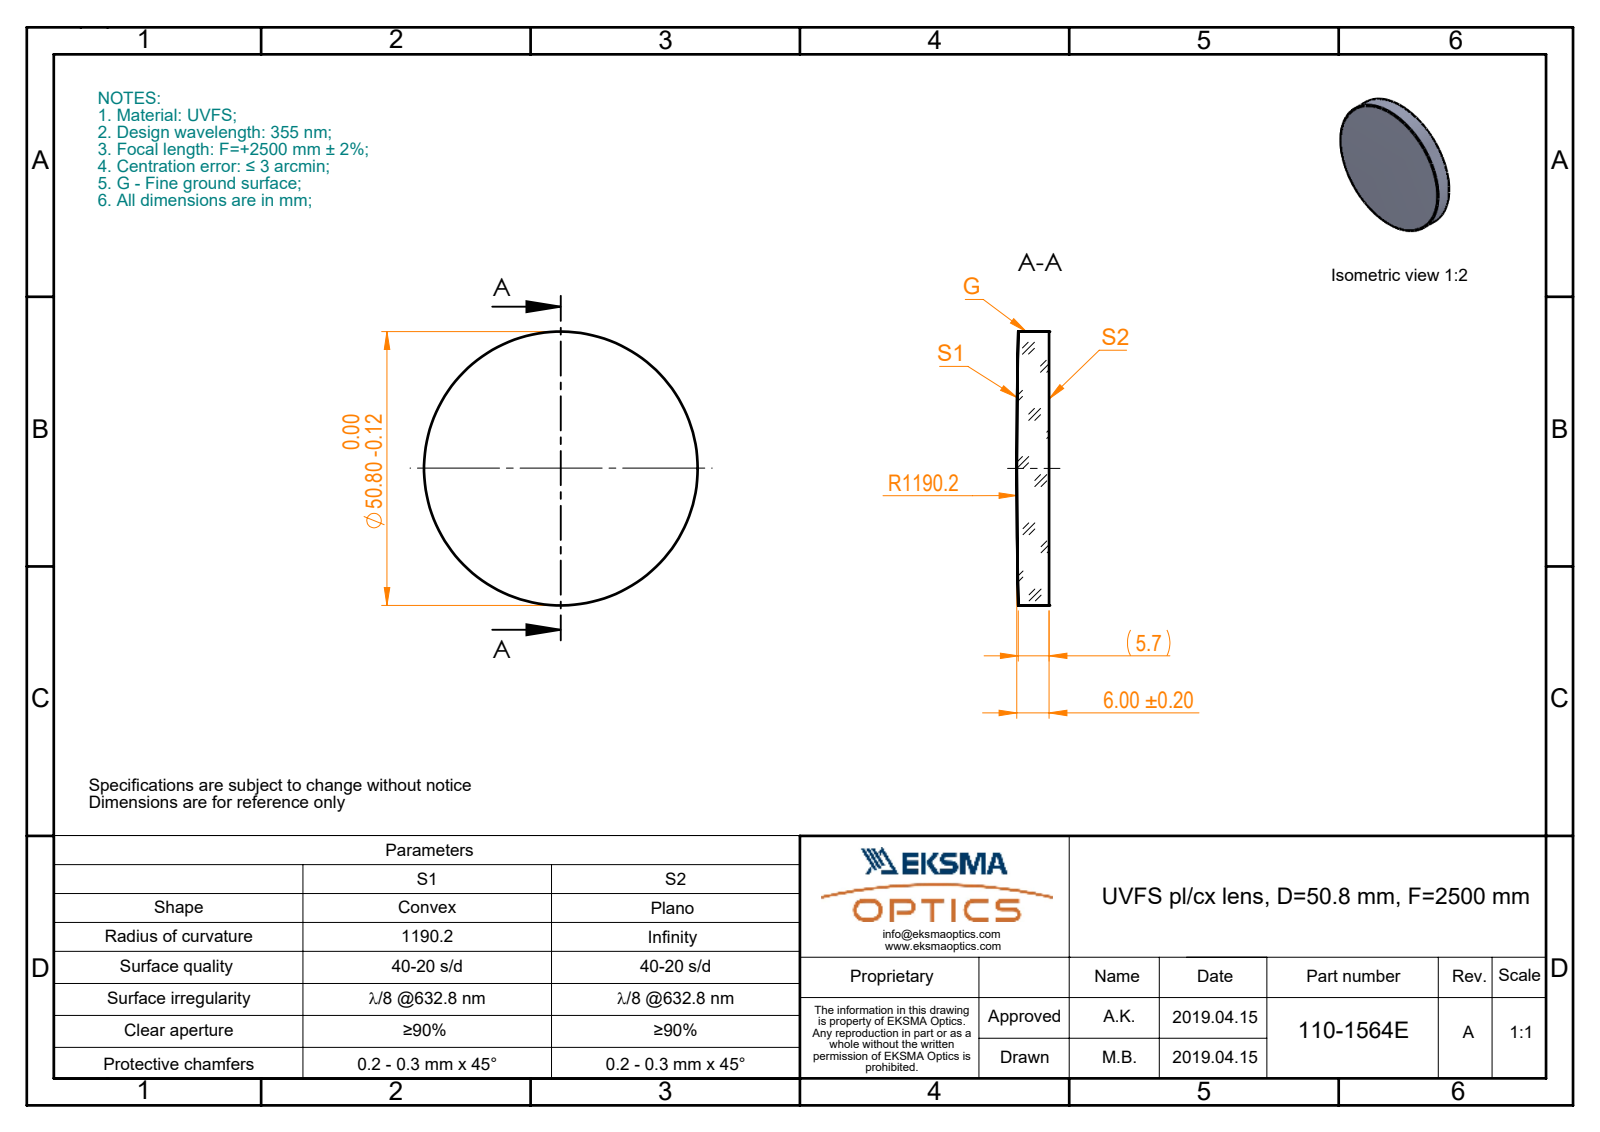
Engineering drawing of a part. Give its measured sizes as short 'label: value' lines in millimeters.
name: 110-1565E UVFS pl-cx 50.8 F2500
written by: SolidWorks 2017 (CONFIG_CONTROL_DESIGN)
unit: mm
bodies: 1 solid, 5 faces (1 planar, 2 cylindrical, 2 other)
size: 50.8 × 50.8 × 6
volume: 11 886 mm³; area: 4 968 mm²
bosses: 1× ⌀50.8
